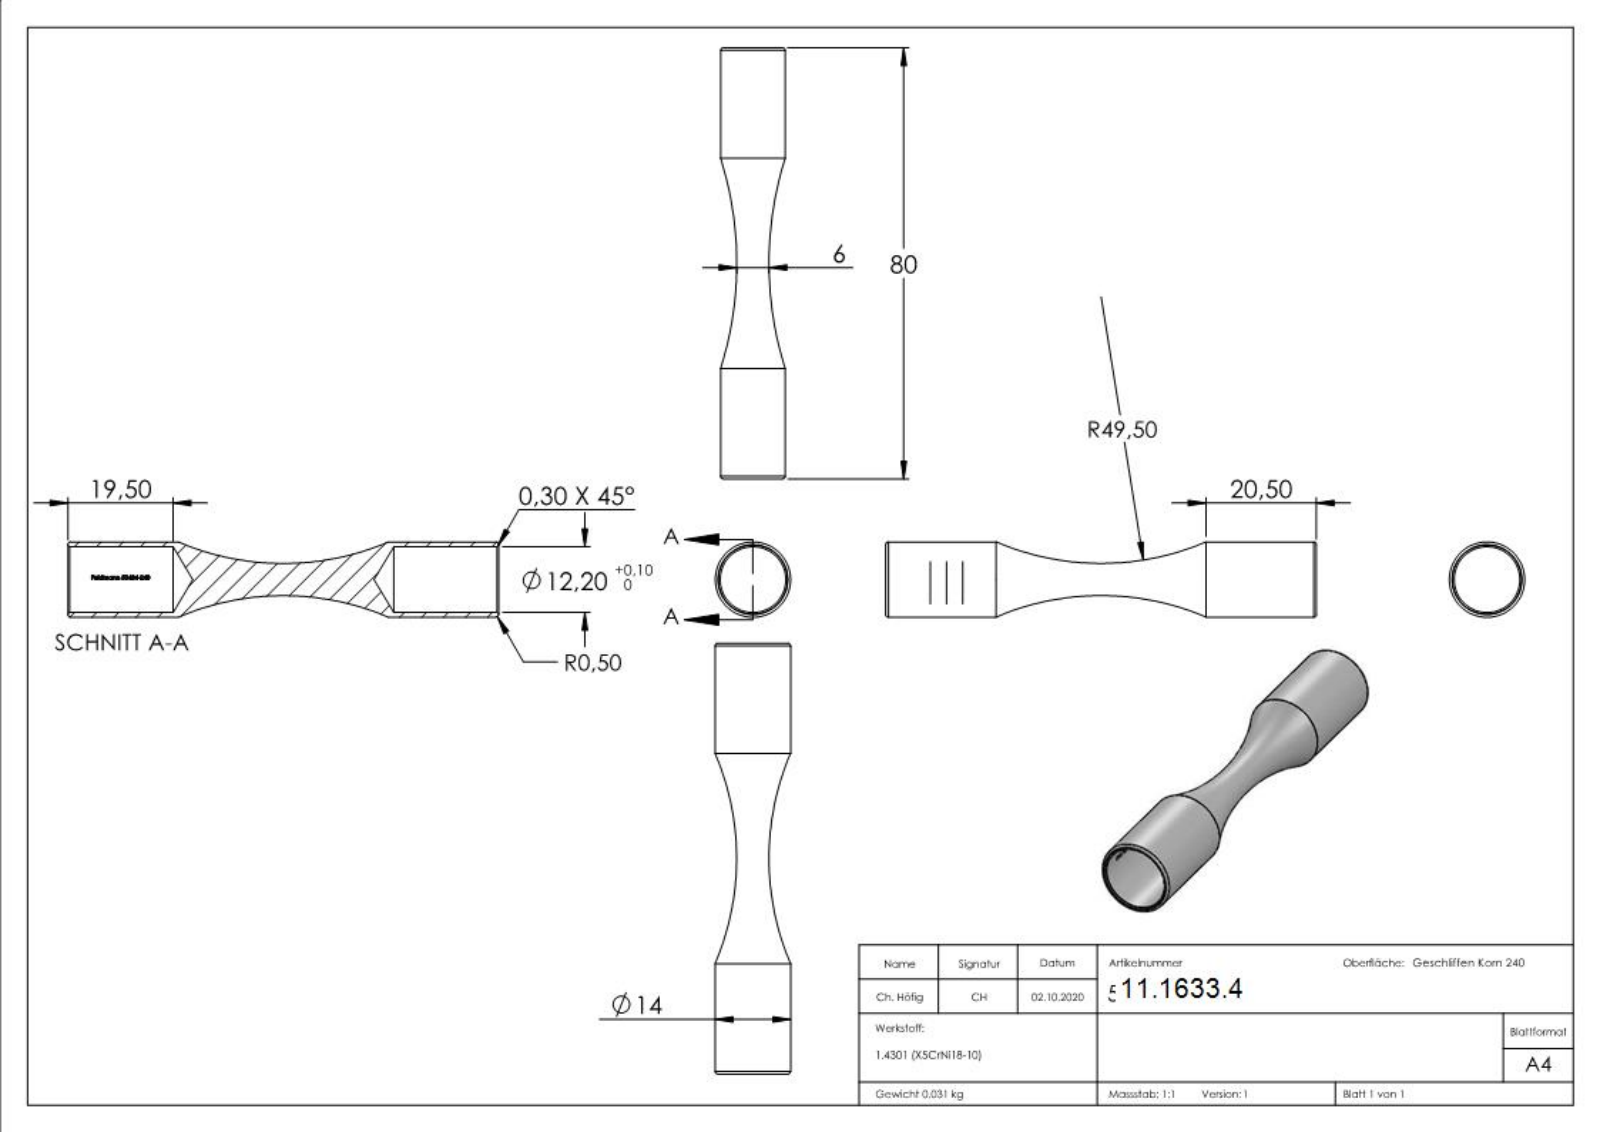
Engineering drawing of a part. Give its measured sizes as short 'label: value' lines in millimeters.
name: 50434-240
written by: SolidWorks 2018 (CONFIG_CONTROL_DESIGN)
unit: mm
bodies: 1 solid, 270 faces (114 planar, 46 cylindrical, 110 other)
size: 79.99 × 14 × 14
volume: 3 907 mm³; area: 4 711 mm²
holes: 1× ⌀12.2
bosses: 1× ⌀14
rounds: 1× R6.2
face distances: 79.98, 1.3, 1.21, 0.53, 6.43, 0.75, 2.81, 8.77, 5.96, 0.44
